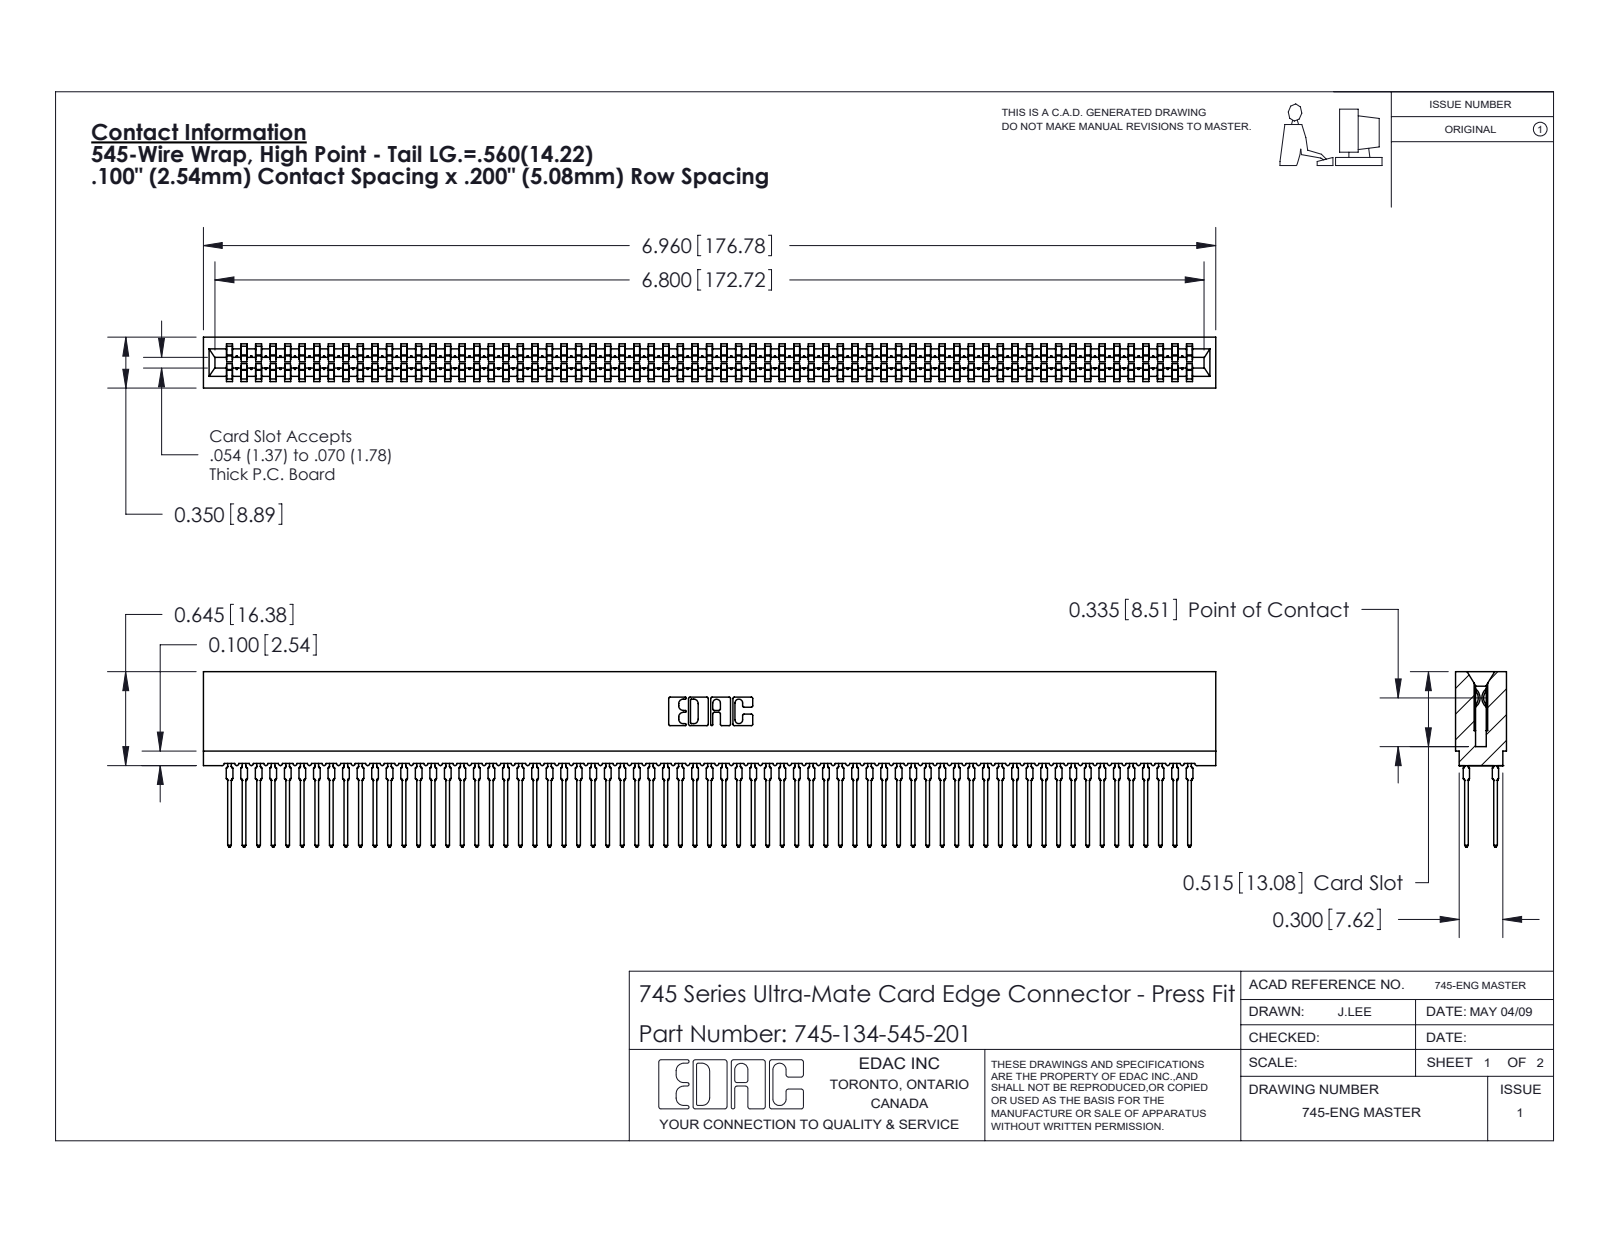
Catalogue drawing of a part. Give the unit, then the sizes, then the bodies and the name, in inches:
Units: inches
Overall size (bounding box): 6.96 × 1.206 × 0.35
Partial cylindrical surfaces — rounded edges, fillets, slot ends (radius × count): R0.021 ×268, R0.015 ×134, R0.01 ×22, R0.005 ×8, R0.011 ×8, R0.007 ×6, R0.031 ×6, R0.026 ×3
Main face-to-face distances: 0.063, 0.287, 0.35, 0.2, 0.045, 0.305, 0.018, 0.243, 0.138, 0.212
Volume: 0.991 in³ · Surface area: 55.24 in²
Bodies: 135 solids, 12088 faces (6219 planar, 2385 cylindrical, 3484 other)
Part name (STEP PRODUCT): 745 Part_Insulator Option - 01; 745-134-545-201; 745-292-001_545
STEP written by: SolidWorks 2020 (CONFIG_CONTROL_DESIGN)
